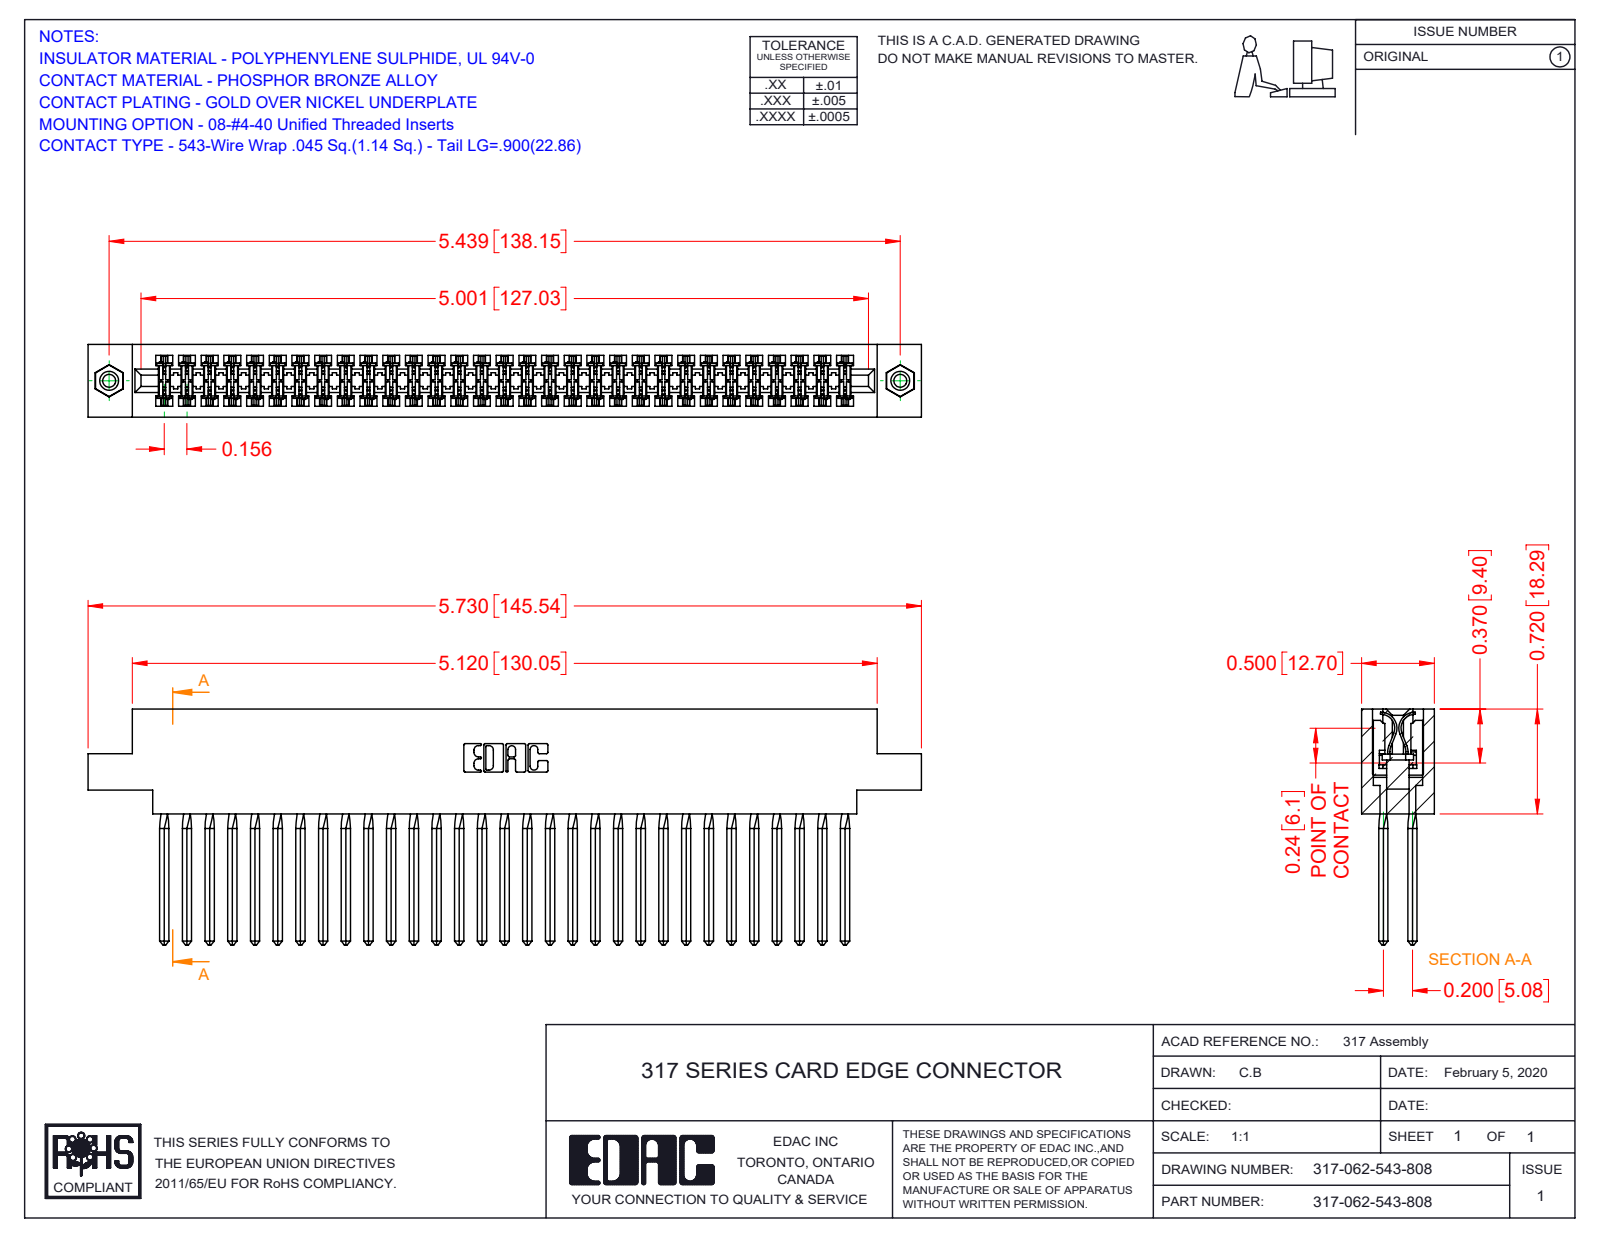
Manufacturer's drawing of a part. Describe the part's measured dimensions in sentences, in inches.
The part is named "345-250-001_345-250-003-102; 317-062-543-878; 317-290-001_543; 317 Part_.156 Dia - TI". Its 3-D file was written by "SolidWorks 2016 (CONFIG_CONTROL_DESIGN)". It is 65 solids with 5680 faces: 4616 planar, 800 cylindrical and 264 other. Overall it measures 5.73 by 1.62 by 0.5 inches. Its volume is 1.486 cubic inches and its surface area 56.64 square inches. Round holes: 2 of diameter 0.089, 2 of diameter 0.125, 2 of diameter 0.156. Round bosses or shafts: 2 of diameter 0.155. Partial cylindrical surfaces (rounded edges, fillets, slot ends): 124 of radius 0.015, 22 of radius 0.01, 6 of radius 0.007, 6 of radius 0.031, 3 of radius 0.026, 2 of radius 0.095, 2 of radius 0.1, 2 of radius 0.11. The main face-to-face distances are 0.5, 0.075, 0.425, 0.35, 0.11, 0.195, 0.094, 0.2, 0.115, 0.131. The hole center spacings are 5.439.
